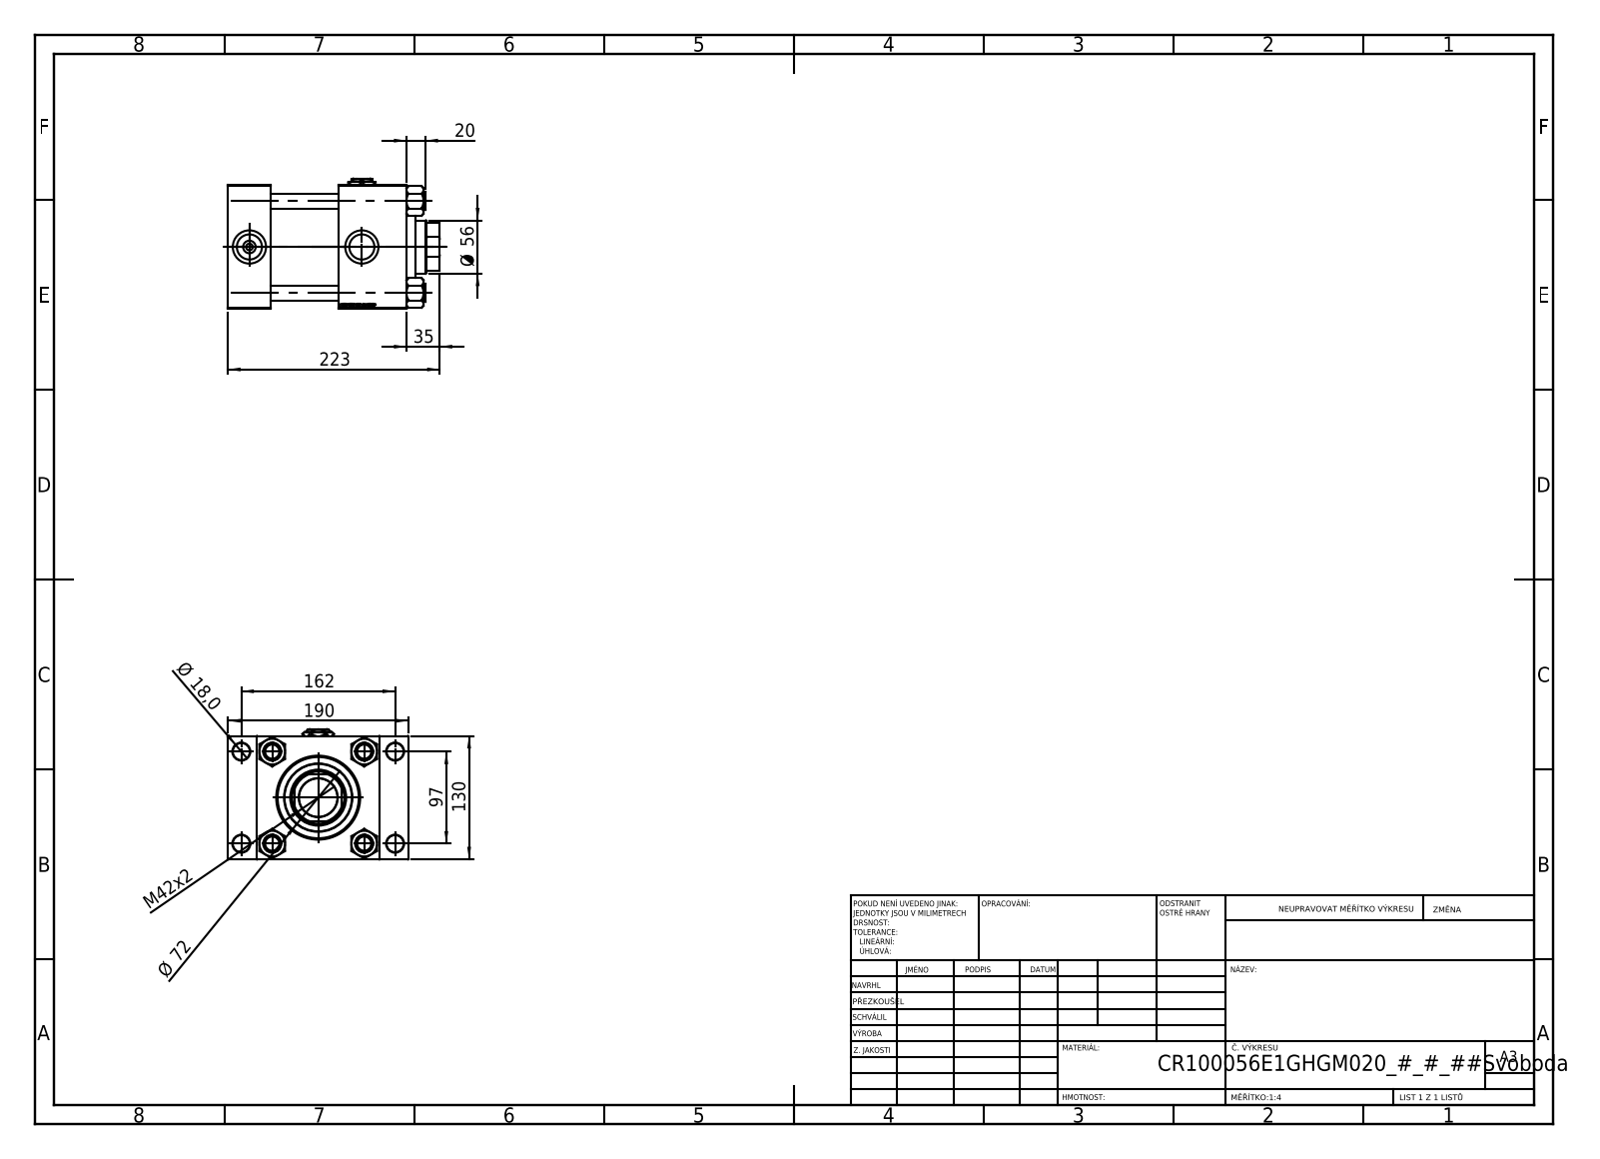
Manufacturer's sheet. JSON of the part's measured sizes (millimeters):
{"part_name": "V215CR_E_Body; Zatka_pro_OIL_PORT; NUT_M5_E; V215_VC_A (+2 more)", "step_written_by": "SolidWorks 2019 (CONFIG_CONTROL_DESIGN)", "units": "millimeters", "bodies": {"solids": 12, "faces": 1231, "planar": 569, "cylindrical": 90, "other": 572}, "overall_size": [223, 190, 137], "volume_mm3": 2784000, "surface_area_mm2": 380358, "round_holes": [[16, 4], [18, 4], [26.44, 3], [35, 3], [7, 2], [40.5, 1], [56, 1], [59, 1], [76, 1], [85.5, 1], [100, 1]], "round_bosses_or_shafts": [[19, 4], [106, 1], [72, 1]], "partial_cylinders_radius": [[27, 1]], "face_to_face_distances": [130, 45, 188, 143, 30, 160, 71, 116, 72, 20], "hole_center_spacings": [32.55, 68.52, 94.41, 96.9, 102.27, 129.45, 161.73, 97]}
